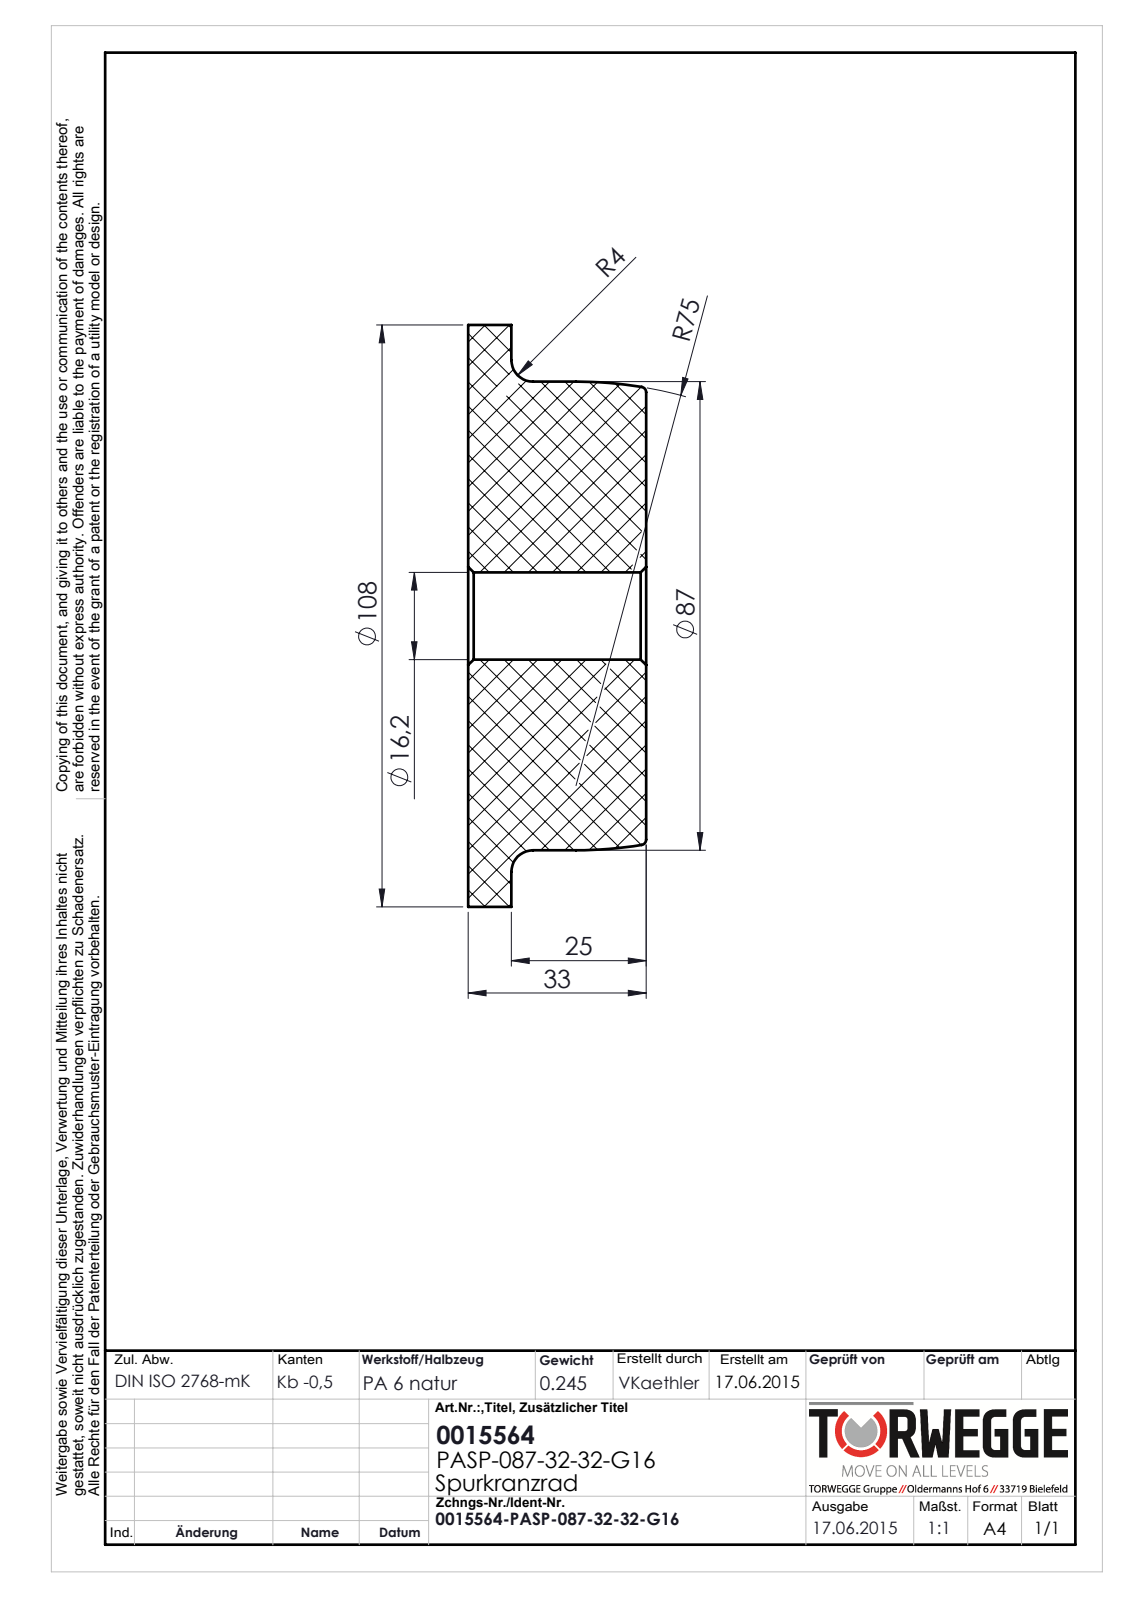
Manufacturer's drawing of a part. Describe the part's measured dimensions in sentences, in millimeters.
The part is named "0015564-PASP-087-32-32-G16". Its 3-D file was written by "SolidWorks 2014 (AUTOMOTIVE_DESIGN)". It is 1 solid with 19 faces: 3 planar, 6 cylindrical and 10 other. Overall it measures 108 by 108 by 33 millimeters. Its volume is 214 606 cubic millimeters and its surface area 28 222 square millimeters. Round holes: 1 of diameter 16.2. Round bosses or shafts: 1 of diameter 108, 1 of diameter 87. The main face-to-face distances are 33, 8, 25.
